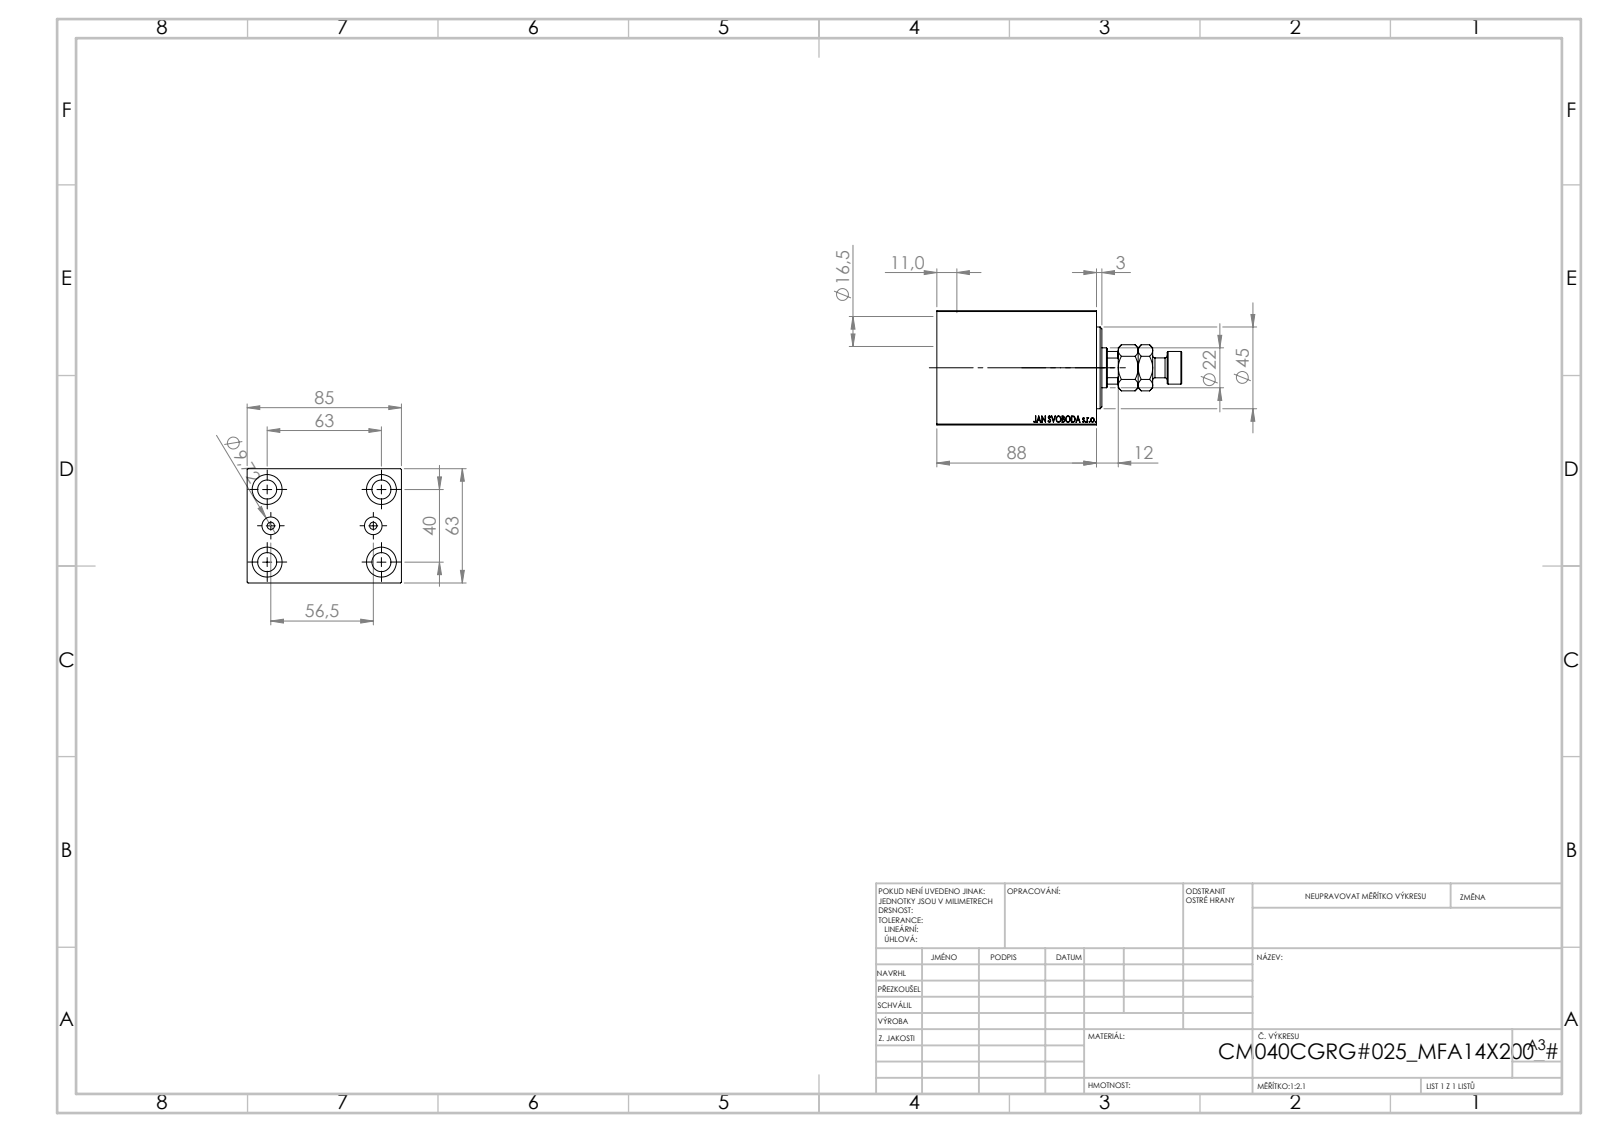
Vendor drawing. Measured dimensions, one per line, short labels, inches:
name: V450CM_VC_B; V450CM_C_VCP; MFA; V450CM_C_Body
written by: SolidWorks 2019 (CONFIG_CONTROL_DESIGN)
unit: in
bodies: 4 solids, 910 faces (424 planar, 60 cylindrical, 426 other)
size: 5.315 × 3.346 × 2.48
volume: 25.62 in³; area: 130.4 in²
holes: 4× ⌀0.413, 4× ⌀0.65, 2× ⌀0.157, 2× ⌀0.383, 1× ⌀0.492, 1× ⌀0.866, 1× ⌀1.004, 1× ⌀1.575, 1× ⌀1.654, 1× ⌀1.772
bosses: 1× ⌀0.709, 1× ⌀0.433
rounds: 1× R0.413
face distances: 2.48, 3.346, 3.465, 0.472, 2.992, 1.126, 1.866, 2.339, 0.433, 3.031
hole spacings: 0.798, 1.469, 2.481, 1.112, 1.575, 2.48, 2.938, 2.224
